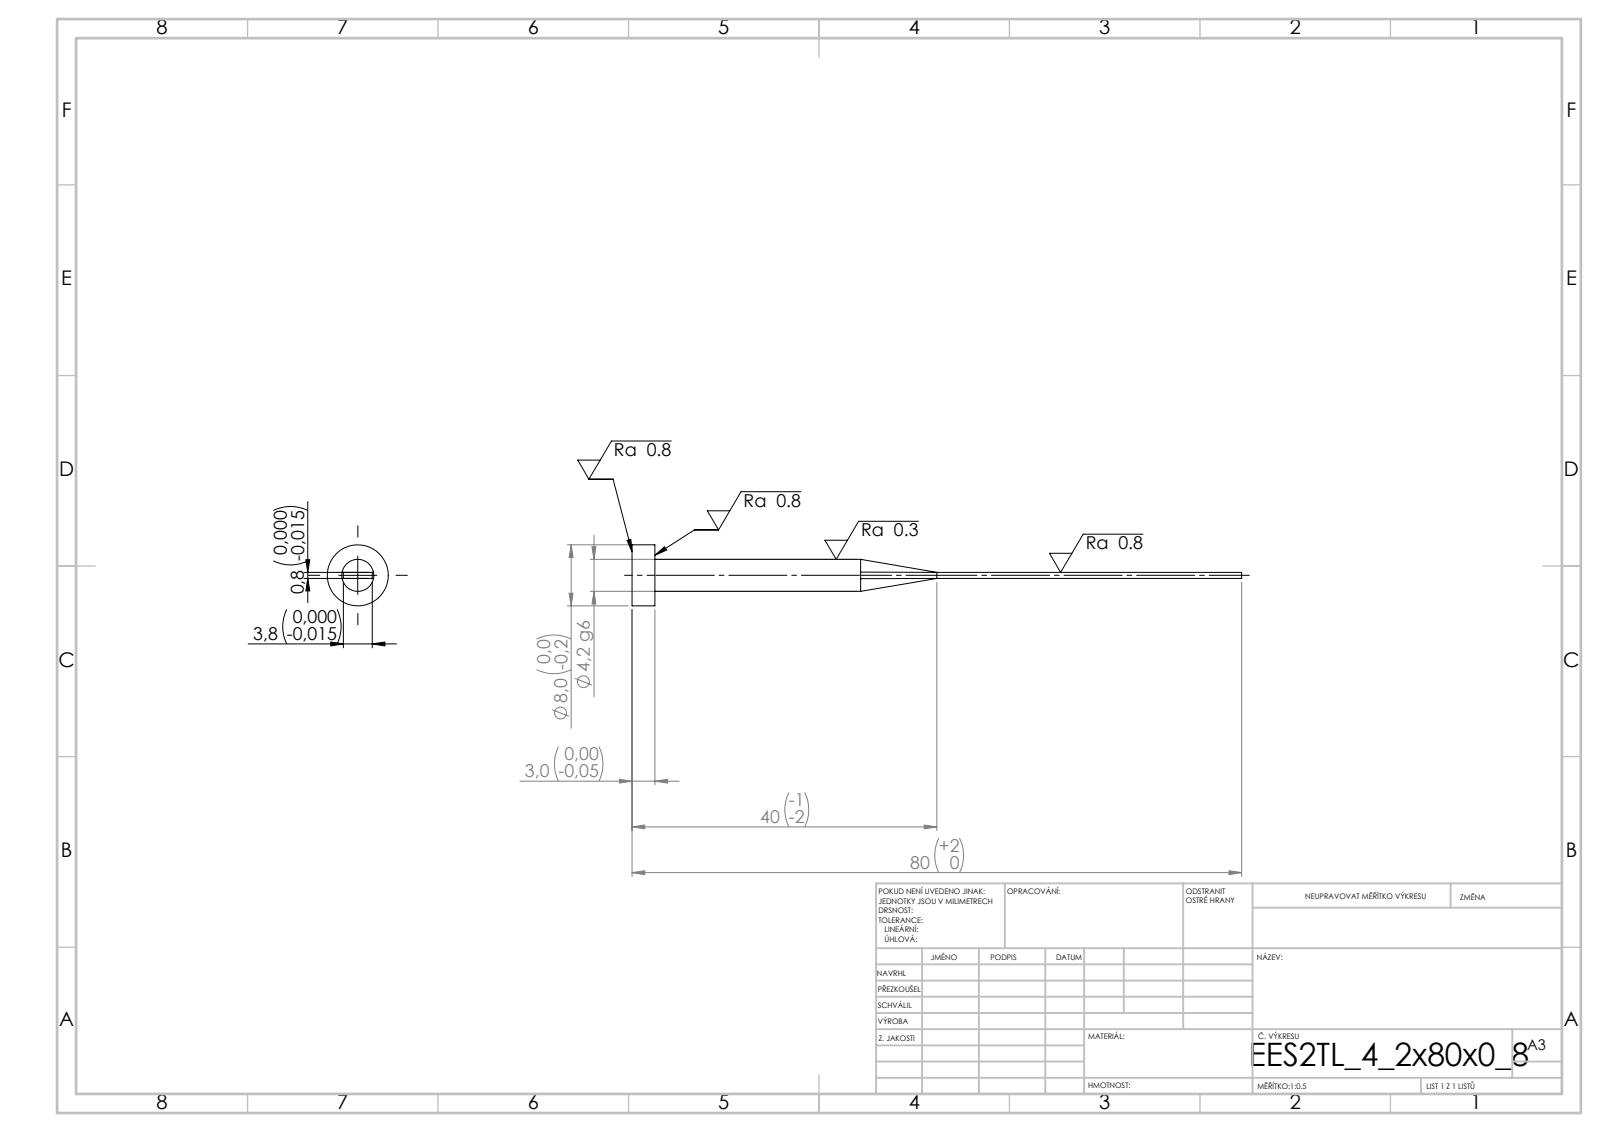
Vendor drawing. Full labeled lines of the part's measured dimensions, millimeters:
STEP written by: SolidWorks 2019 (CONFIG_CONTROL_DESIGN)
Units: millimetres
Bodies: 1 solid, 15 faces (7 planar, 4 cylindrical, 4 other)
Overall size (bounding box): 80 × 8 × 8
Volume: 726 mm³ · Surface area: 997 mm²
Round bosses / shafts (diameter × count): ⌀8 ×1, ⌀4.2 ×1
Main face-to-face distances: 0.8, 3, 3.8, 80, 77
